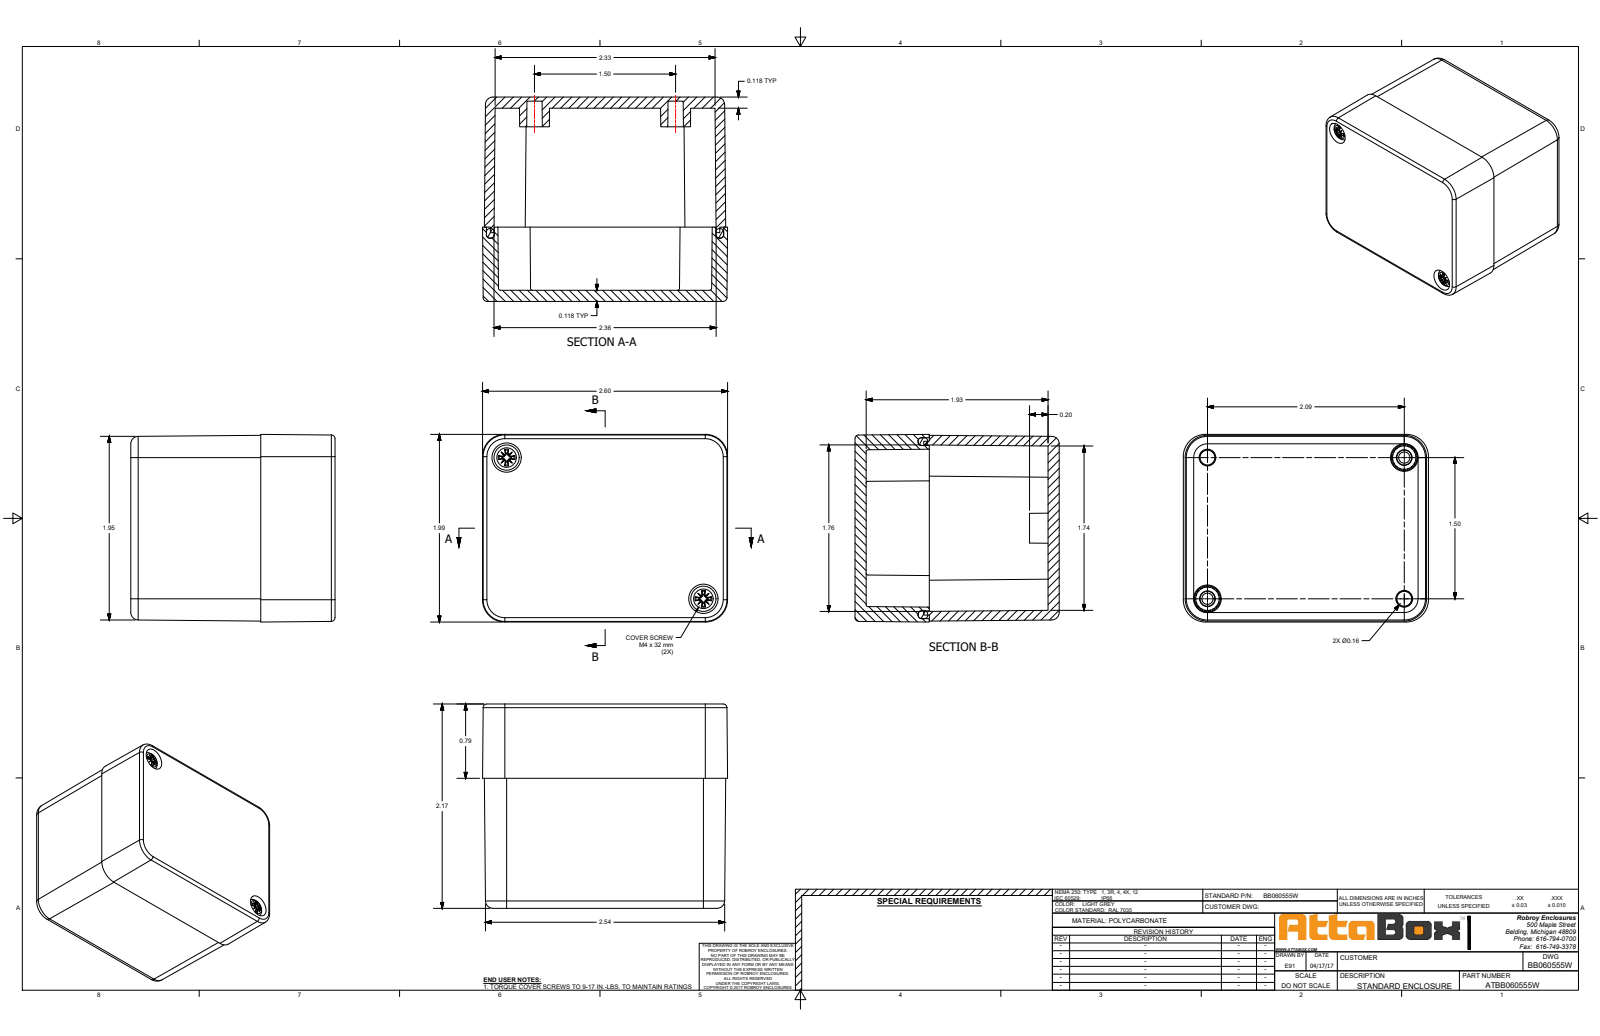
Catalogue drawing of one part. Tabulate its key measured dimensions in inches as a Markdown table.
| quantity | value |
| --- | --- |
| part name | BB060555W |
| STEP written by | SolidWorks 2018 (AUTOMOTIVE_DESIGN) |
| units | inches |
| bodies | 7 solids, 961 faces (341 planar, 250 cylindrical, 370 other) |
| overall size | 2.598 × 2.165 × 1.988 |
| volume | 3.62 in³ |
| surface area | 67.47 in² |
| round holes (diameter × count) | 0.177 × 4, 0.291 × 4, 0.128 × 2, 0.193 × 2, 0.201 × 2, 0.276 × 2, 0.311 × 2 |
| round bosses / shafts (diameter × count) | 0.268 × 2, 0.173 × 2, 0.157 × 2, 0.13 × 2 |
| partial cylindrical surfaces (radius × count) | 0.035 × 48, 0.02 × 8, 0.098 × 8, 0.181 × 8, 0.039 × 4, 0.079 × 4, 0.114 × 4, 0.197 × 4 |
| main face-to-face distances | 0.118, 2.047, 0.102, 2.165, 1.929, 1.876, 1.978, 2.476, 2.579, 1.378 |
| hole center spacings | 1.496, 2.087, 2.568 |
